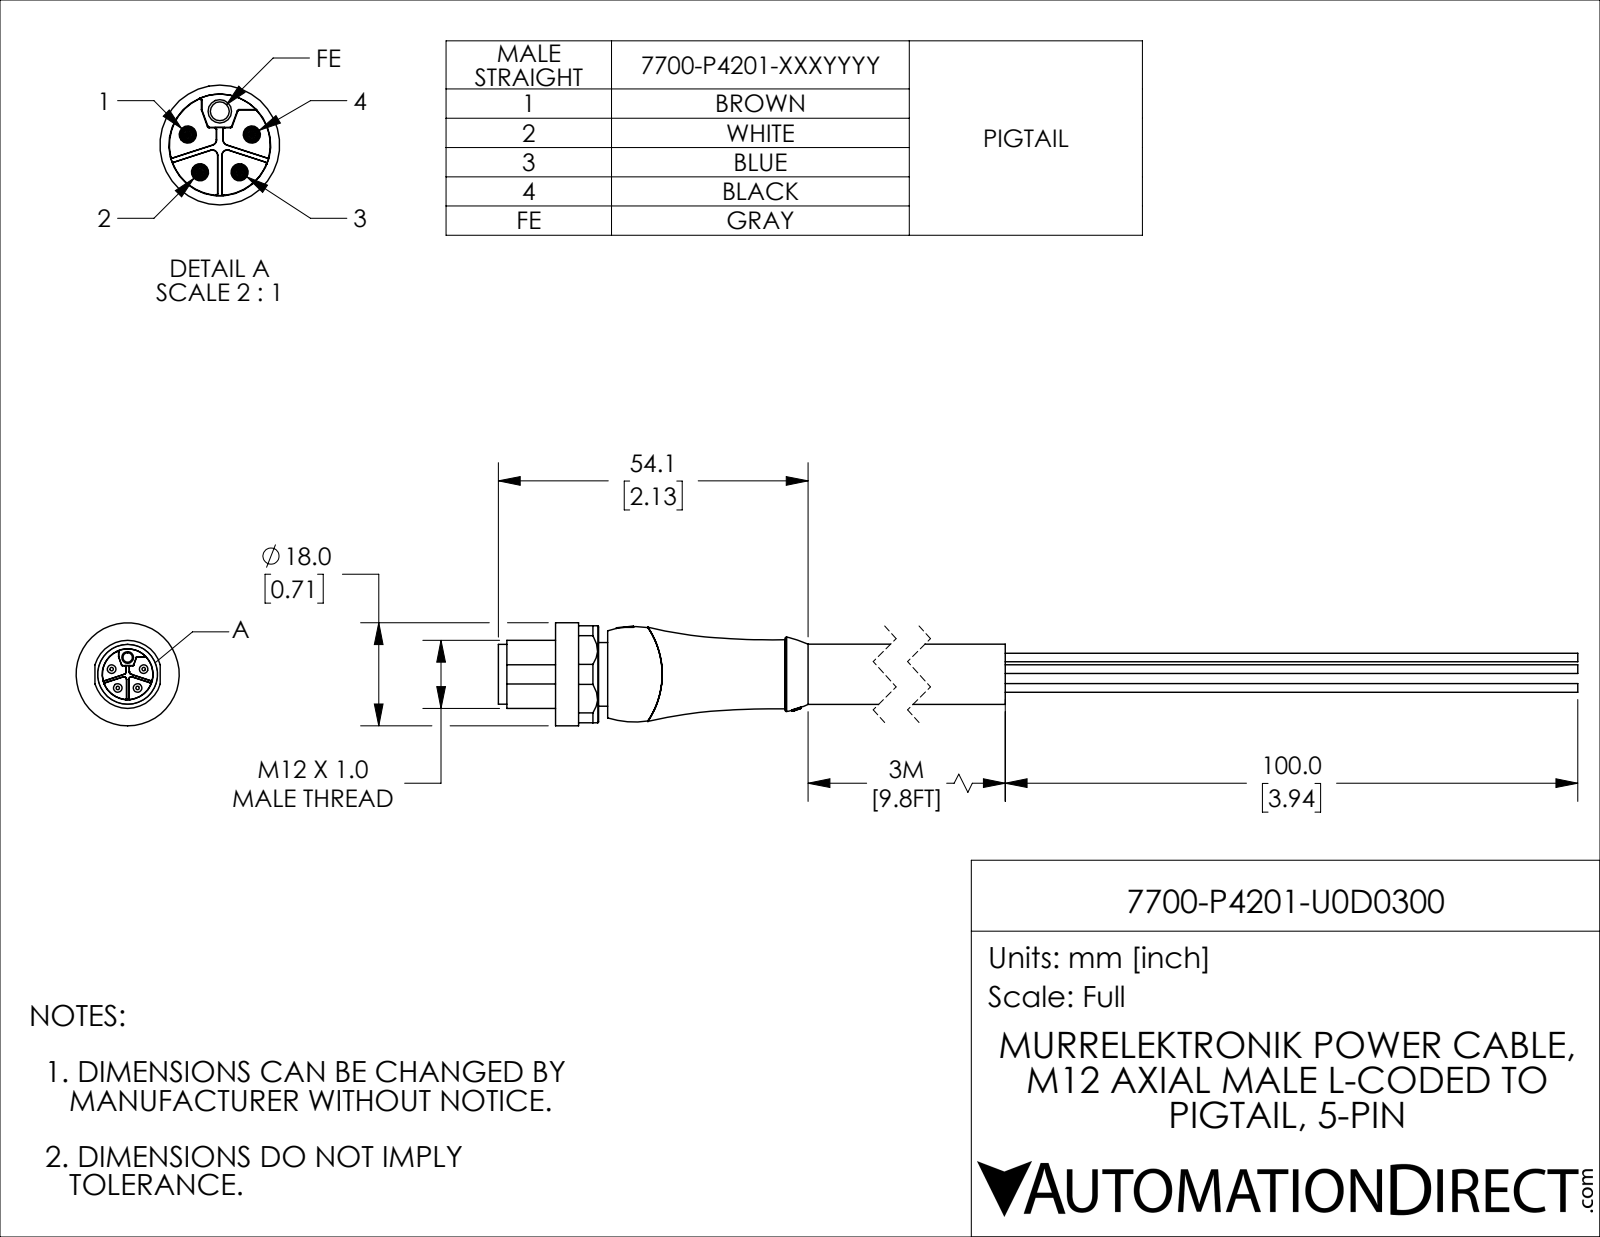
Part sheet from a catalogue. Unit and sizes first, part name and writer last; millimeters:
Units: millimetres
Overall size (bounding box): 254.1 × 18 × 18
Round holes (diameter × count): ⌀1.65 ×1
Round bosses / shafts (diameter × count): ⌀1.5 ×5, ⌀18 ×1, ⌀11.88 ×1, ⌀11.1 ×1, ⌀10.5 ×1, ⌀10.45 ×1
Partial cylindrical surfaces — rounded edges, fillets, slot ends (radius × count): R0.15 ×6, R1.13 ×1, R8.95 ×1
Main face-to-face distances: 9.1, 1.9, 7.2, 144.1, 136.9, 135, 16.94, 1.2, 8.4, 10.3
Volume: 17 489 mm³ · Surface area: 9 110 mm²
Bodies: 1 solid, 190 faces (87 planar, 51 cylindrical, 52 other)
Part name (STEP PRODUCT): 7700-P4201-U0D0300
STEP written by: SolidWorks 2021 (CONFIG_CONTROL_DESIGN)
